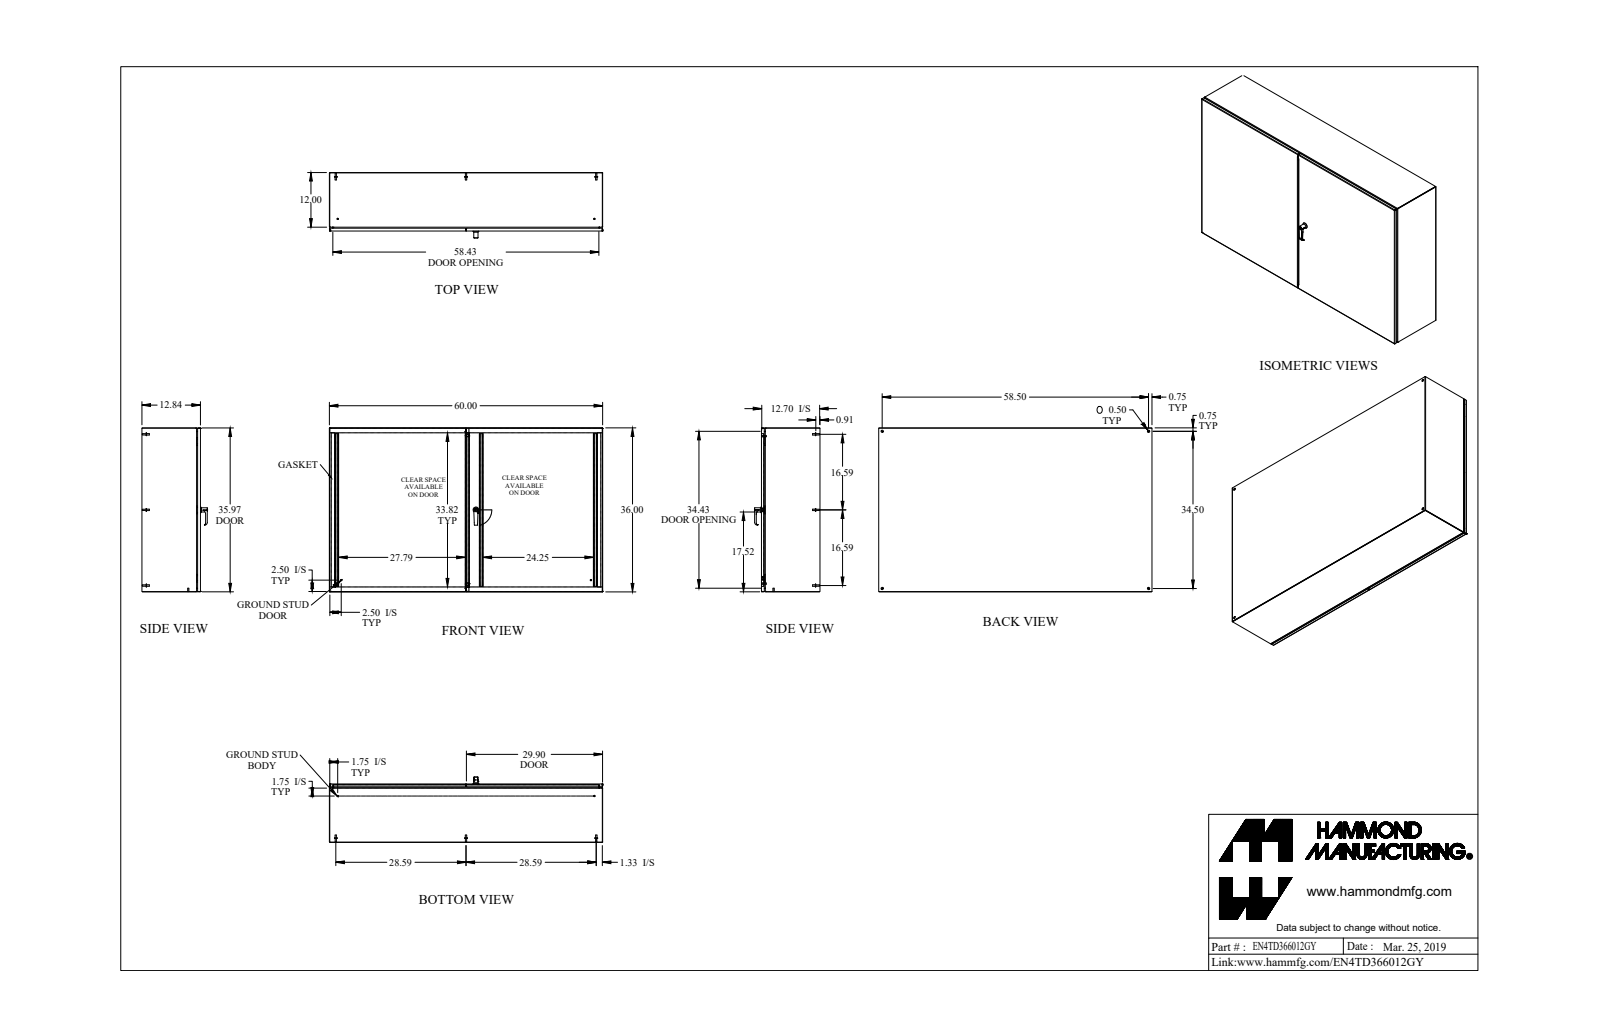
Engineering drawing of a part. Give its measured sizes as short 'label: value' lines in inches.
name: EN4TD366012GY
written by: SolidWorks 2018 (AUTOMOTIVE_DESIGN)
unit: in
bodies: 93 solids, 2351 faces (1082 planar, 854 cylindrical, 415 other)
size: 60 × 36 × 14.372
volume: 579.8 in³; area: 15 564 in²
holes: 6× ⌀0.196, 4× ⌀0.176, 4× ⌀0.5, 3× ⌀0.24, 3× ⌀0.242, 3× ⌀0.25, 3× ⌀0.265, 2× ⌀0.172, 2× ⌀0.256, 2× ⌀0.26, 2× ⌀0.265, 2× ⌀0.275
bosses: 9× ⌀0.25, 8× ⌀0.625, 8× ⌀0.313, 8× ⌀0.27, 4× ⌀0.51, 4× ⌀0.375, 4× ⌀0.281, 4× ⌀0.156
rounds: 30× R0.043, 30× R0.081, 26× R0.036, 26× R0.108, 25× R0.063, 20× R0.094, 16× R0.02, 15× R0.016
face distances: 0.072, 12.77, 12.698, 12.842, 35.928, 59.928, 35.856, 36, 59.856, 60
hole spacings: 0.787, 26.792, 31.748, 32.11, 34.5, 35.841, 58.5, 67.915
